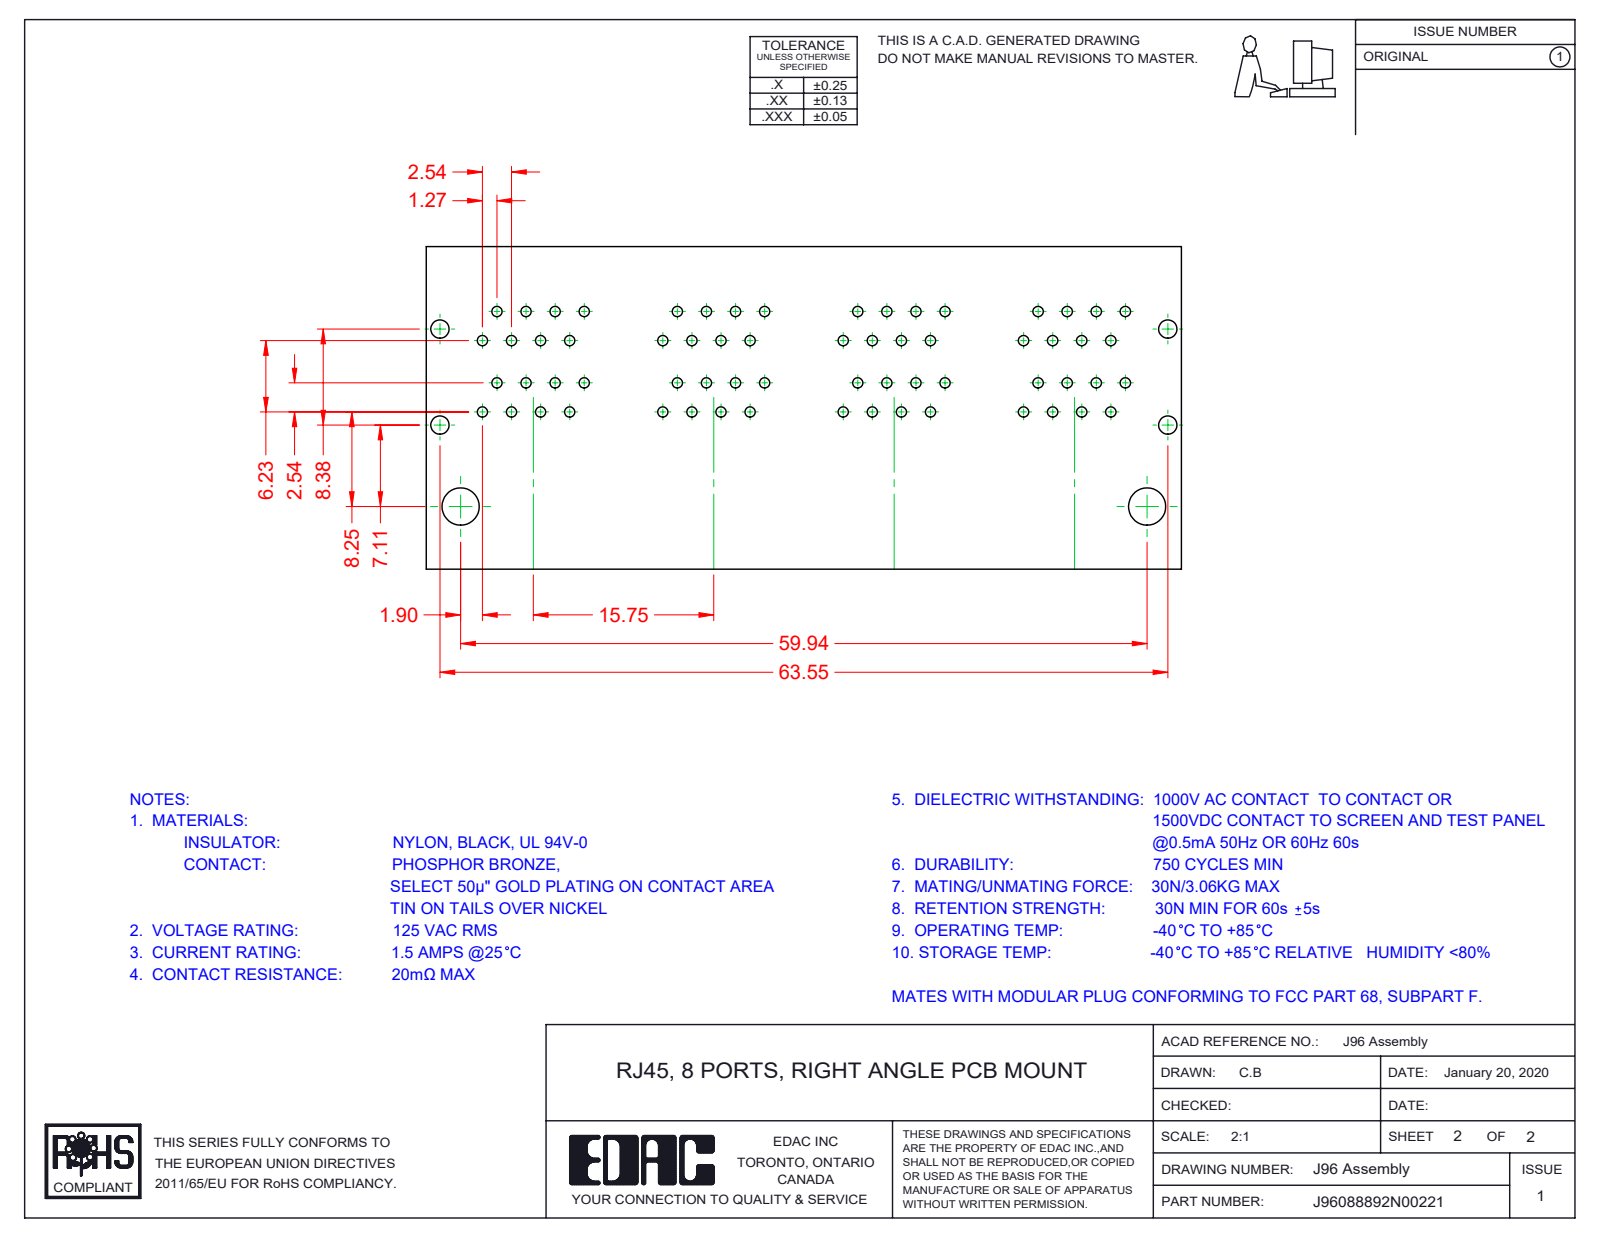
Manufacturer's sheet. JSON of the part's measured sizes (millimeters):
{"part_name": "96 Shield_8 Ports No LED - EMI; 96 Contacts Upper; 96 Insulator Insert; J96088892N00221 (+6 more)", "step_written_by": "SolidWorks 2016 (CONFIG_CONTROL_DESIGN)", "units": "millimeters", "bodies": {"solids": 80, "faces": 7404, "planar": 5801, "cylindrical": 1292, "other": 311}, "overall_size": [67.35, 31.38, 28.15], "volume_mm3": 23548, "surface_area_mm2": 61107, "round_holes": [[1.7, 3]], "round_bosses_or_shafts": [[1.68, 3]], "partial_cylinders_radius": [[0.25, 124], [0.35, 73], [1, 72], [0.5, 49], [0.91, 32], [0.2, 27], [0.27, 14], [0.7, 11]], "face_to_face_distances": [15.75, 0.35, 9.95, 27.95, 1.17, 1.6, 0.54, 9.98, 10.18, 12.67], "hole_center_spacings": [15.75, 31.5]}
